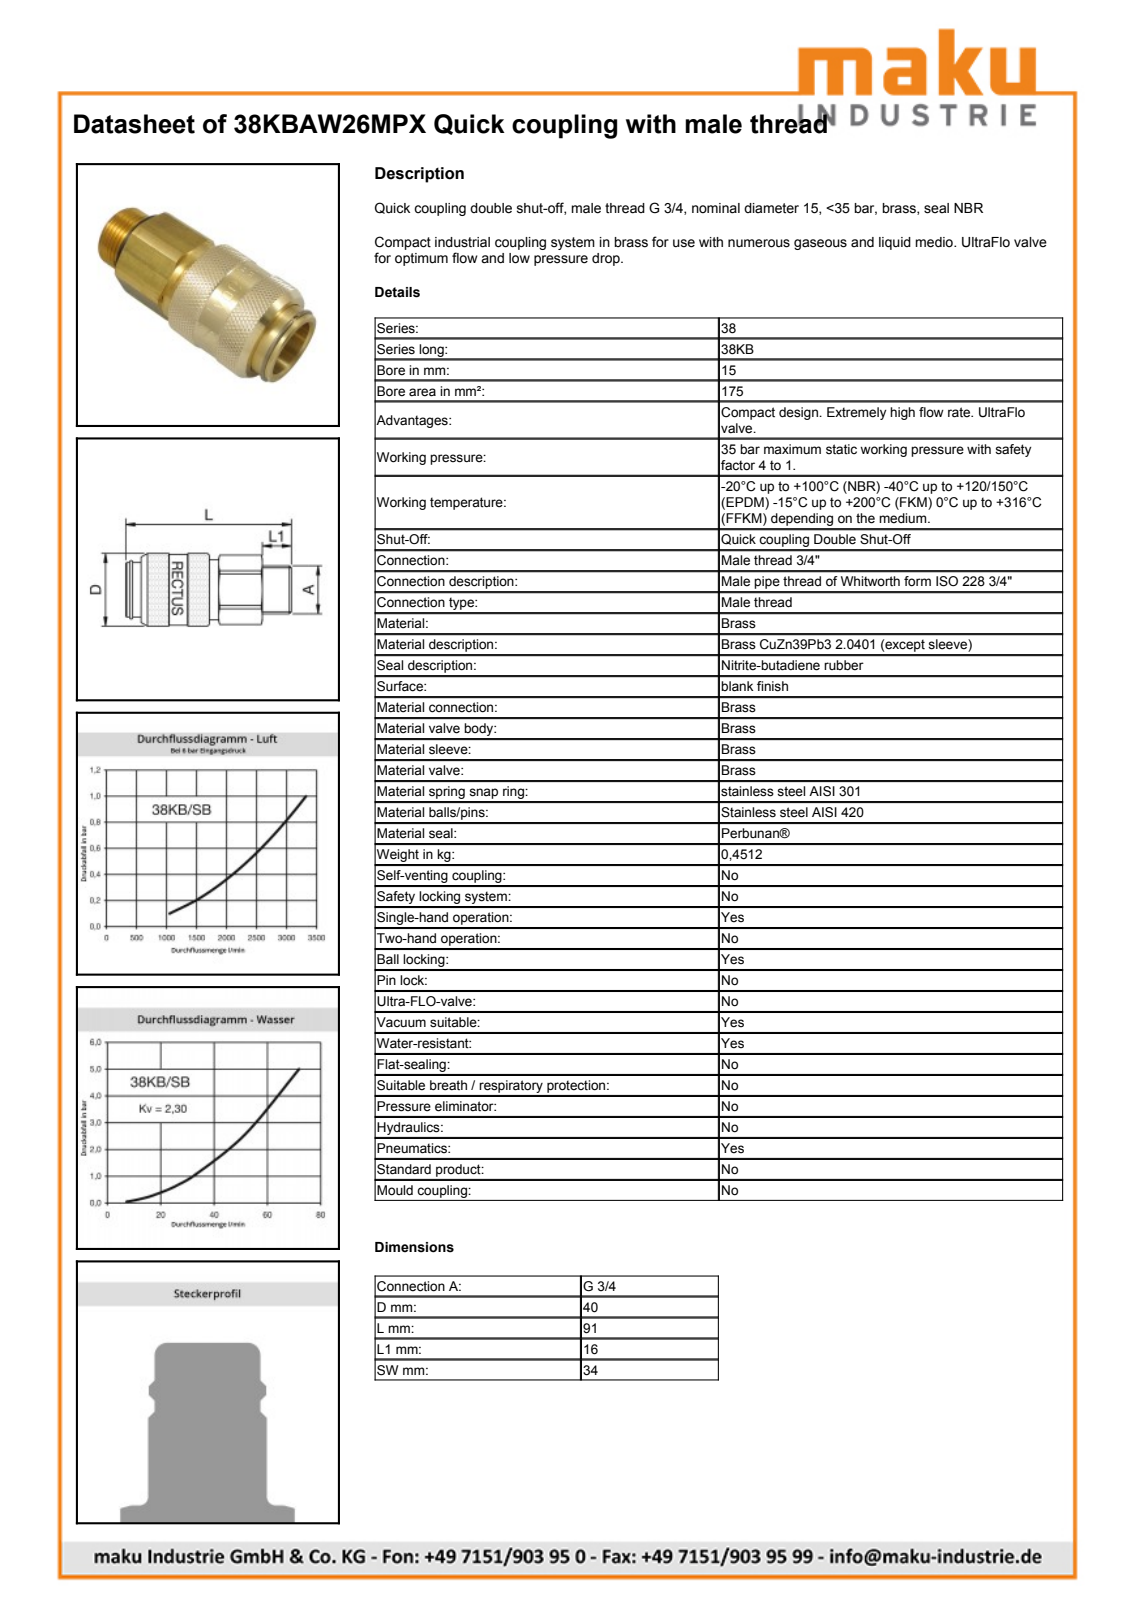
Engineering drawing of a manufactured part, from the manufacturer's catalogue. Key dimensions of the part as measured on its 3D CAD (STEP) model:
Part name (STEP PRODUCT): D105994
STEP written by: Autodesk Inventor 2011 (AUTOMOTIVE_DESIGN)
Units: millimetres
Bodies: 2 solids, 532 faces (195 planar, 79 cylindrical, 258 other)
Overall size (bounding box): 91.25 × 40 × 40
Volume: 85 316 mm³ · Surface area: 21 495 mm²
Round holes (diameter × count): ⌀28.95 ×1, ⌀30 ×1, ⌀30.75 ×1, ⌀34.45 ×1, ⌀34.6 ×1
Round bosses / shafts (diameter × count): ⌀40 ×1, ⌀39 ×1, ⌀34 ×1, ⌀32 ×1, ⌀28.5 ×1, ⌀26.55 ×1, ⌀26.44 ×1
Partial cylindrical surfaces — rounded edges, fillets, slot ends (radius × count): R13.3 ×1, R18.5 ×1, R19.4 ×1
Main face-to-face distances: 34, 91.25, 8.15, 83.1, 77.25, 69.1, 14, 16, 45.6, 40.25
